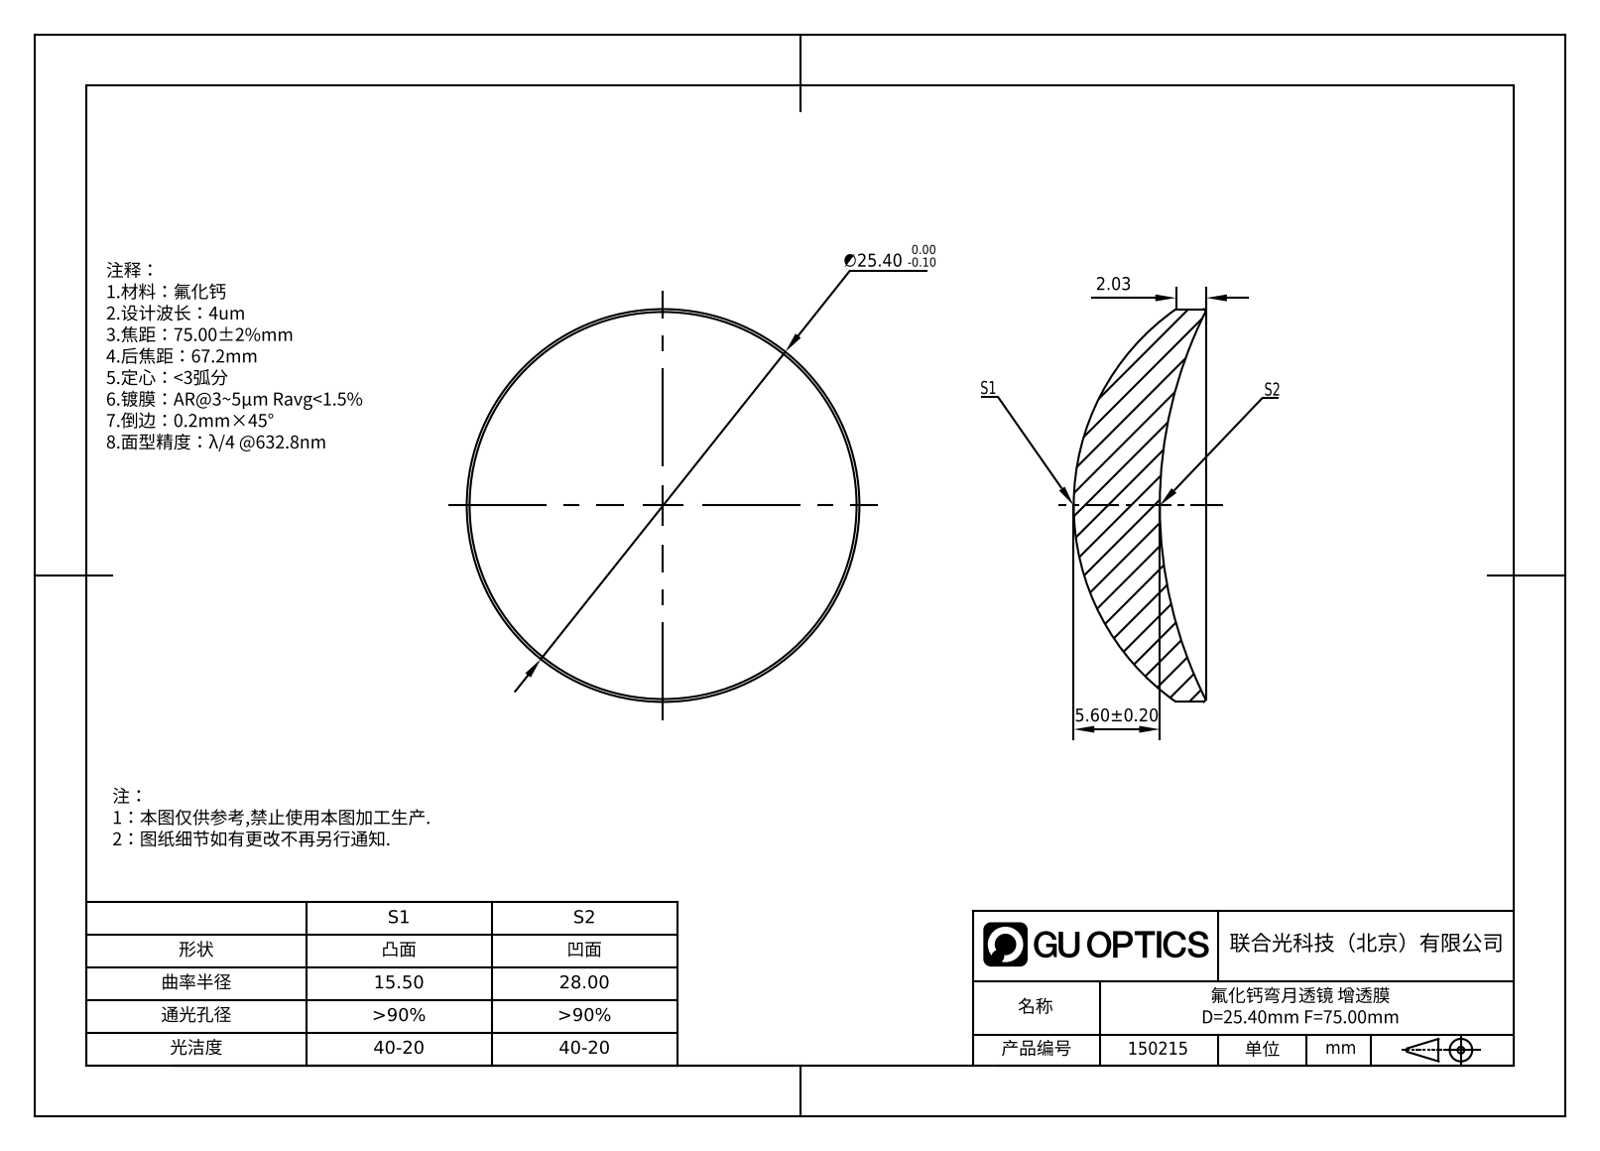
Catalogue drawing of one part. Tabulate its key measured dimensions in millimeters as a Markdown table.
| quantity | value |
| --- | --- |
| part name | GLM5-025B-075-IR1 |
| STEP written by | SolidWorks 2022 (AUTOMOTIVE_DESIGN) |
| units | millimeters |
| bodies | 1 solid, 8 faces (0 planar, 2 cylindrical, 6 other) |
| overall size | 25.4 × 25.4 × 8.55 |
| volume | 2 053 mm³ |
| surface area | 1 327 mm² |
| round bosses / shafts (diameter × count) | 25.4 × 1 |
